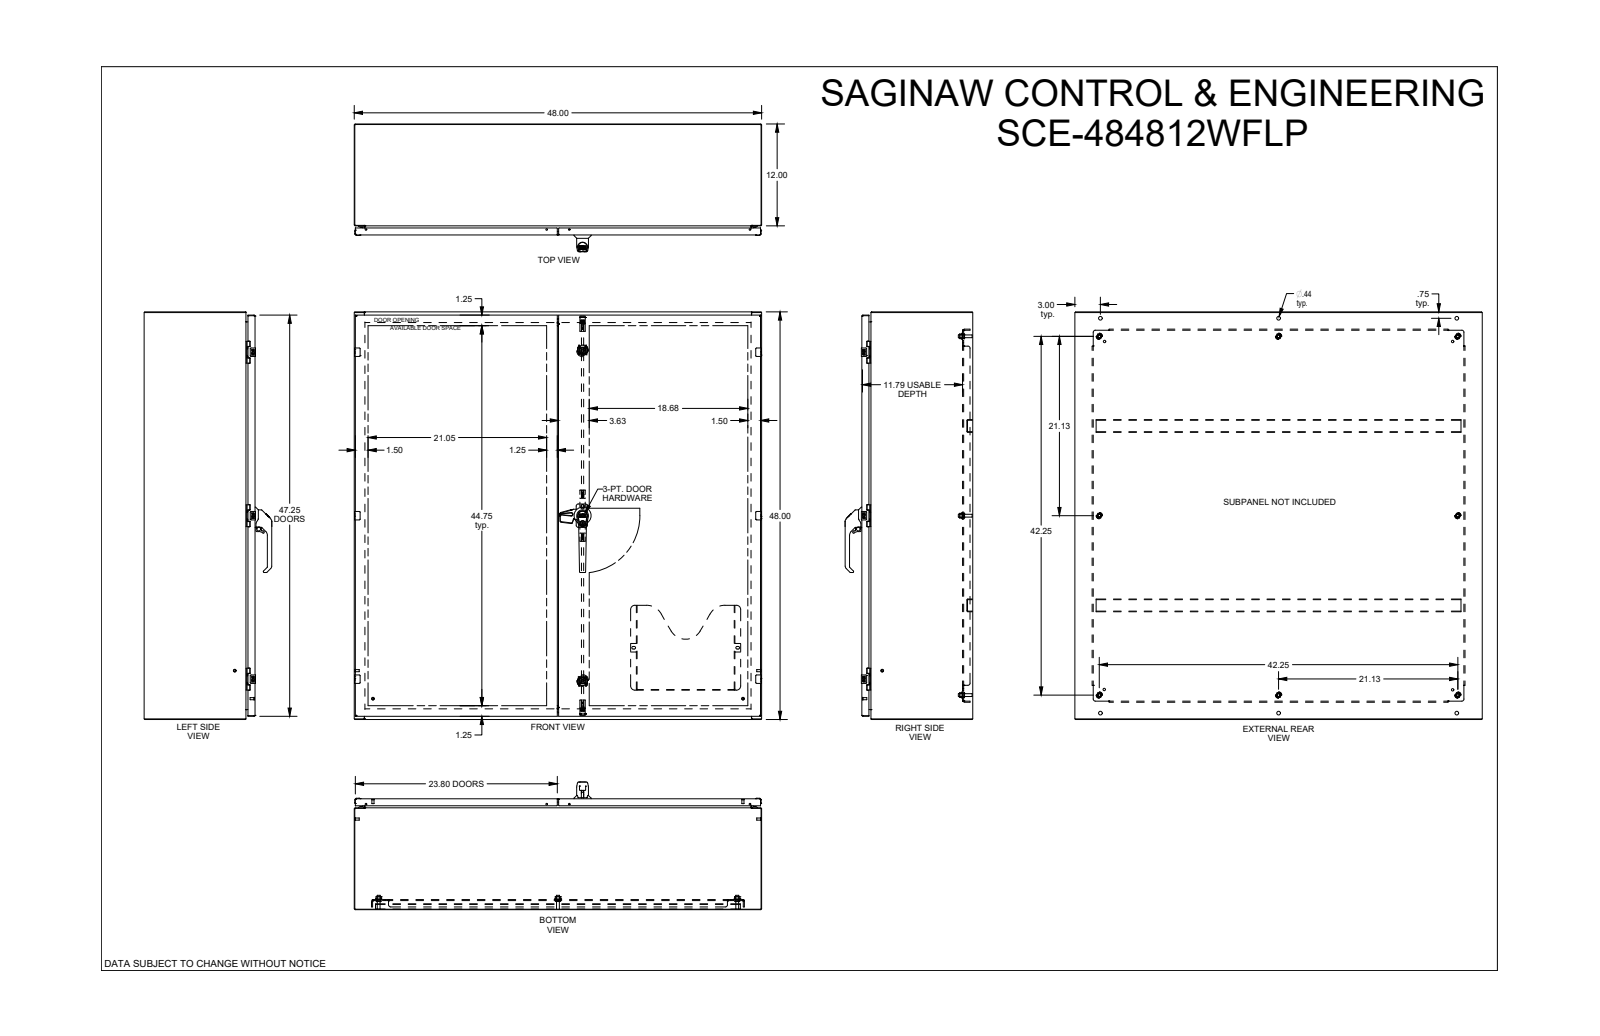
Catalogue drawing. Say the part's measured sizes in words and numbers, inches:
The part is named "MODEL-319-BDY; MODEL-319-TP; MODEL-319-BTM; MODEL-319-MSTR (+8 more)". Its 3-D file was written by "CREO PARAMETRIC BY PTC INC, 2017260 (AUTOMOTIVE_DESIGN)". It is 125 solids with 8859 faces: 3324 planar, 2584 cylindrical and 2951 other. Overall it measures 48 by 48 by 15.048 inches. Its volume is 909.9 cubic inches and its surface area 20 669 square inches. Round holes: 14 of diameter 0.266, 12 of diameter 0.172, 12 of diameter 0.205, 12 of diameter 0.244, 12 of diameter 0.375, 8 of diameter 0.367, 8 of diameter 0.5, 6 of diameter 0.04, 6 of diameter 0.156, 6 of diameter 0.218, 6 of diameter 0.437, 4 of diameter 0.17. Round bosses or shafts: 18 of diameter 0.17, 12 of diameter 0.25, 12 of diameter 0.24, 8 of diameter 0.366, 8 of diameter 0.332, 8 of diameter 0.196, 7 of diameter 0.248, 4 of diameter 0.563. Partial cylindrical surfaces (rounded edges, fillets, slot ends): 130 of radius 0.03, 87 of radius 0.015, 64 of radius 0.01, 64 of radius 0.02, 50 of radius 0.005, 36 of radius 0.02, 33 of radius 0.04, 31 of radius 0.039. The main face-to-face distances are 0.075, 12.993, 12.918, 47.925, 13.068, 1.125, 1.2, 11.868, 11.793, 0.125. The hole center spacings are 19.25, 38.5, 50.211, 0.985, 46.374, 46.385, 4.133, 4.996.
